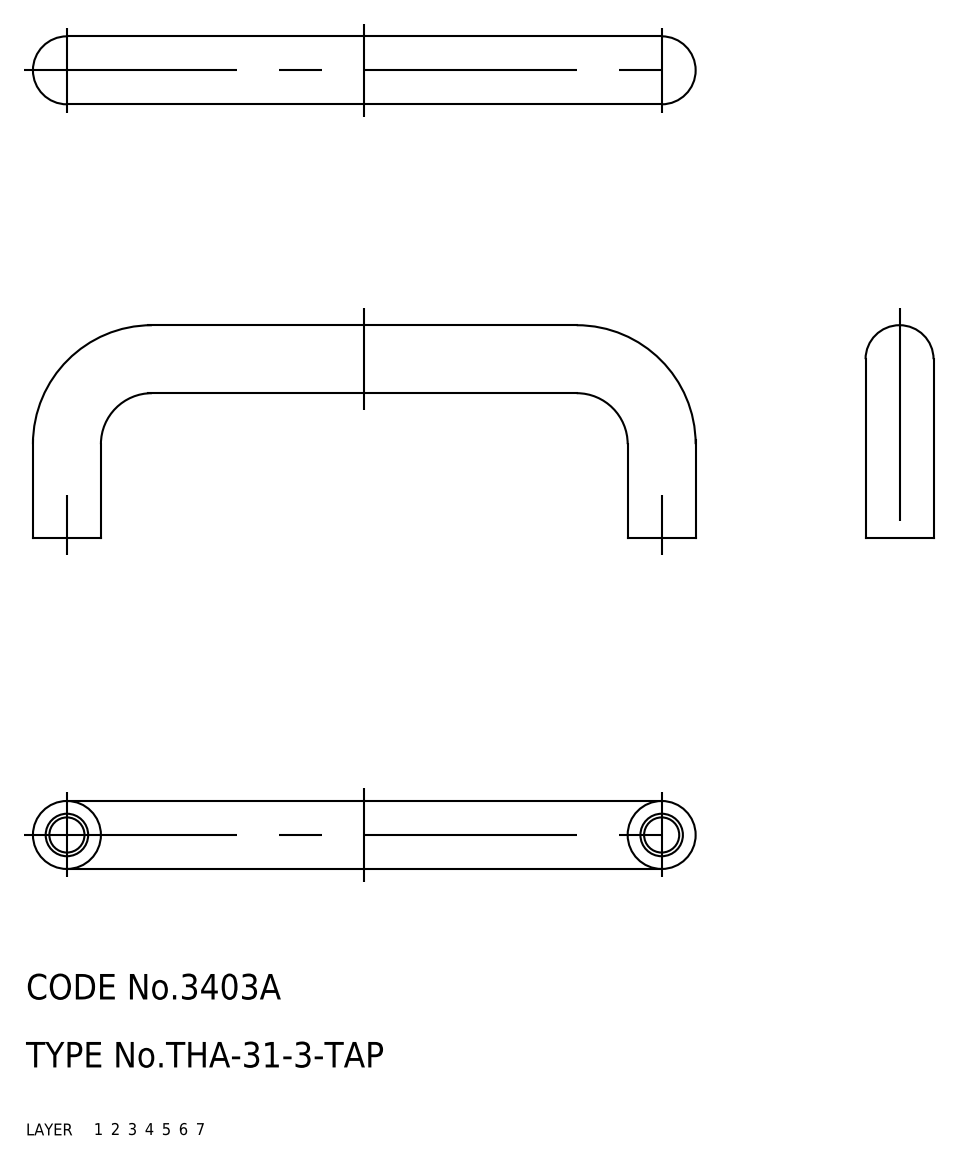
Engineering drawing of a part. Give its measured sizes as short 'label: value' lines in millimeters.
name: pull
written by: CADfix (AUTOMOTIVE_DESIGN)
unit: mm
bodies: 1 solid, 18 faces (0 planar, 0 cylindrical, 18 other)
size: 78 × 25 × 8
volume: 4 817 mm³; area: 3 016 mm²
